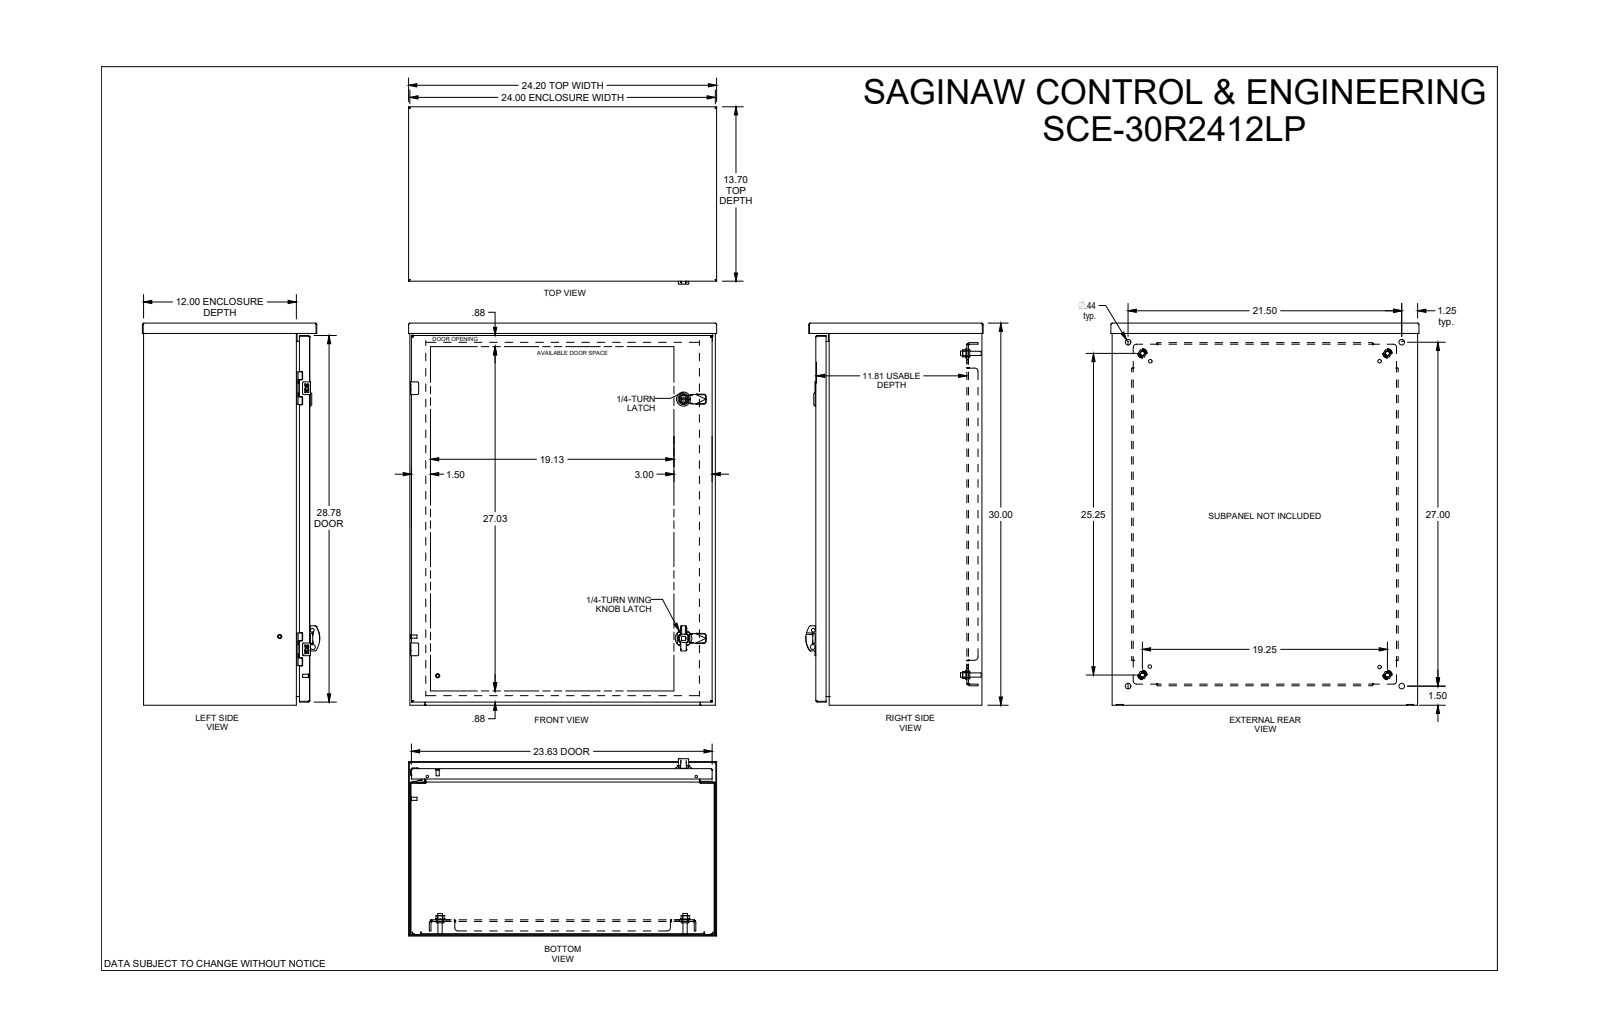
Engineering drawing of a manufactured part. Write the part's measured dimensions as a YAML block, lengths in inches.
part_name: "SCE-30R2412LP"
step_written_by: "SolidWorks 2019 (CONFIG_CONTROL_DESIGN)"
units: inches
bodies: {solids: 0, faces: 2429, planar: 1160, cylindrical: 823, other: 446}
overall_size: [30, 24.2, 13.927]
round_holes:
  - {diameter: 0.172, count: 4}
  - {diameter: 0.205, count: 4}
  - {diameter: 0.244, count: 4}
  - {diameter: 0.266, count: 4}
  - {diameter: 0.281, count: 4}
  - {diameter: 0.367, count: 4}
  - {diameter: 0.375, count: 4}
  - {diameter: 0.438, count: 4}
  - {diameter: 0.5, count: 4}
  - {diameter: 0.04, count: 2}
  - {diameter: 0.156, count: 2}
  - {diameter: 0.188, count: 2}
round_bosses_or_shafts:
  - {diameter: 0.17, count: 6}
  - {diameter: 0.366, count: 4}
  - {diameter: 0.332, count: 4}
  - {diameter: 0.25, count: 4}
  - {diameter: 0.24, count: 4}
  - {diameter: 0.196, count: 3}
  - {diameter: 0.866, count: 2}
  - {diameter: 0.802, count: 2}
partial_cylinders:
  - {radius: 0.015, count: 72}
  - {radius: 0.012, count: 60}
  - {radius: 0.01, count: 26}
  - {radius: 0.02, count: 24}
  - {radius: 0.112, count: 23}
  - {radius: 0.06, count: 22}
  - {radius: 0.052, count: 19}
  - {radius: 0.03, count: 15}
face_to_face_distances: [0.06, 0.06, 12.933, 12.993, 23.94, 13.053, 12.993, 0.125, 1, 29.94]
hole_center_spacings: [20.5, 0.024, 0.493, 0.875, 0.985, 20.394, 2.296, 18.641]
